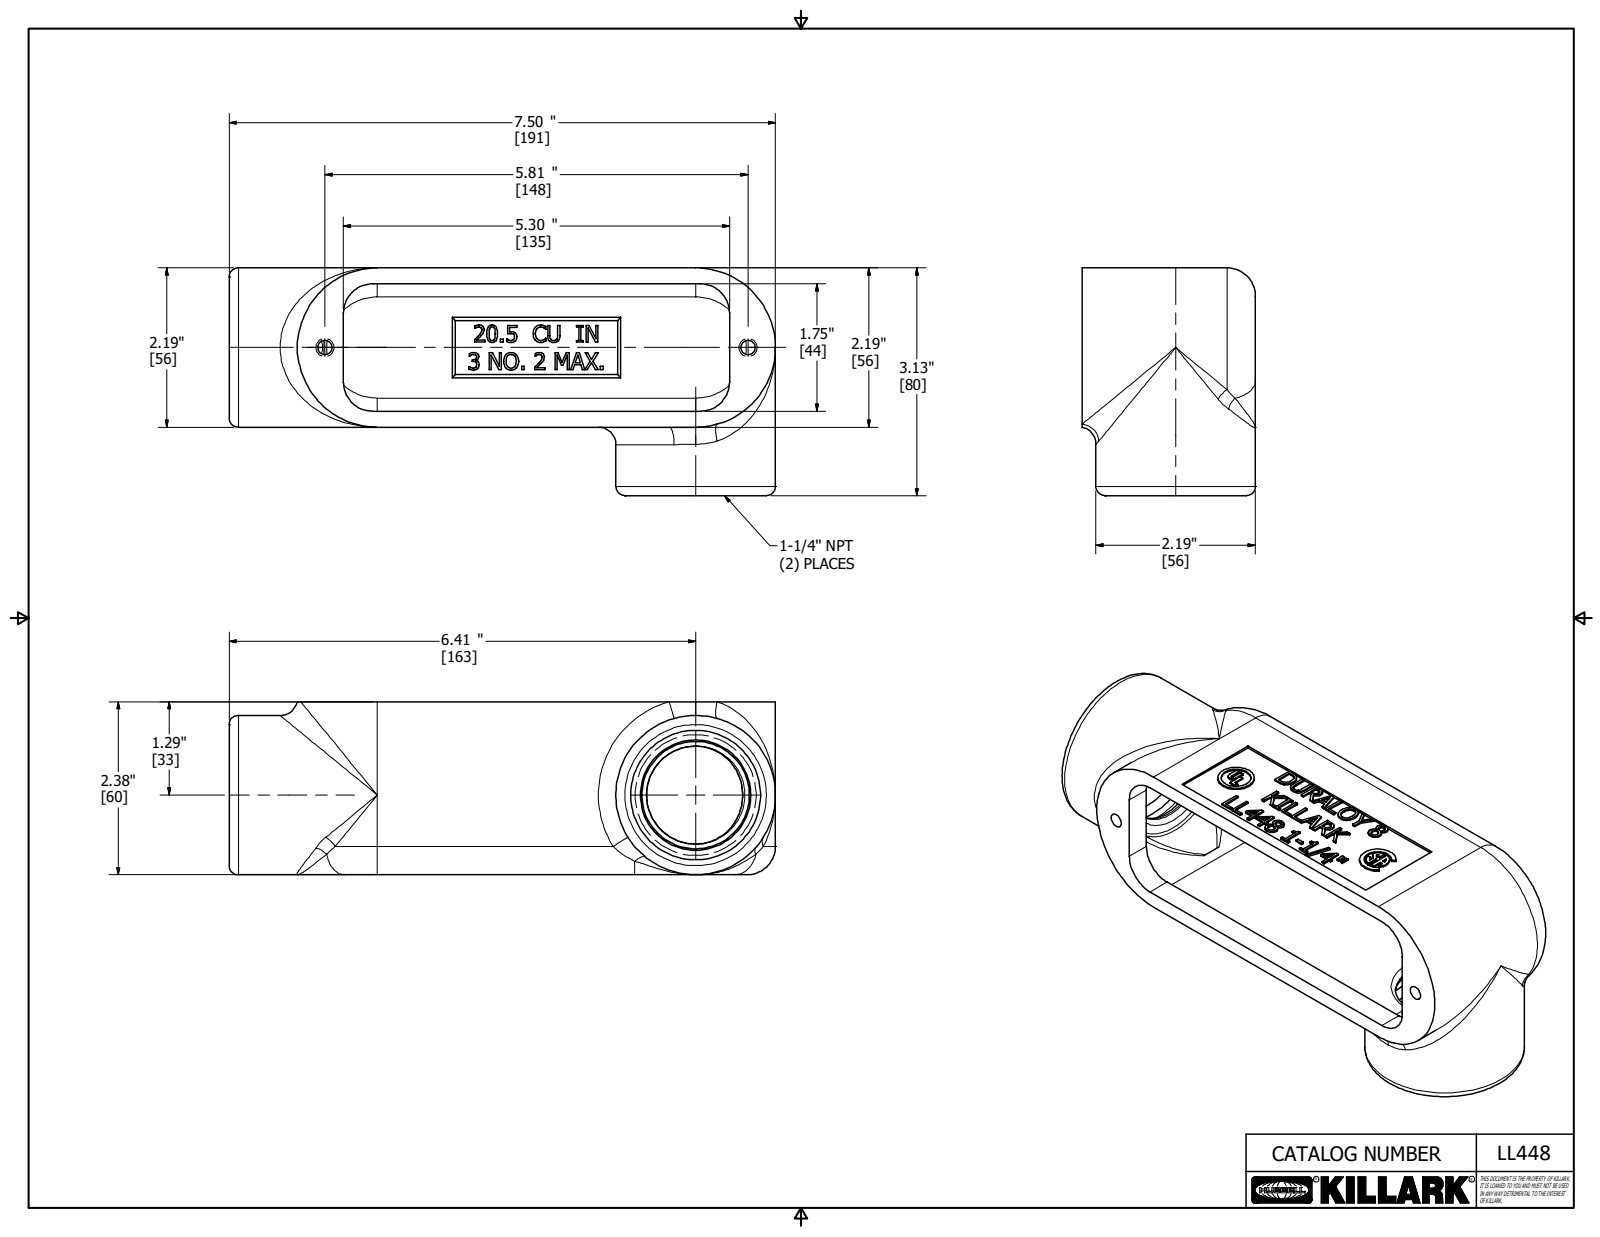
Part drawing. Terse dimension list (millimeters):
name: 21727-2
written by: Autodesk Inventor 2018 (AUTOMOTIVE_DESIGN)
unit: mm
bodies: 1 solid, 722 faces (447 planar, 36 cylindrical, 239 other)
size: 190.5 × 79.5 × 60.5
volume: 207 500 mm³; area: 74 710 mm²
holes: 2× ⌀5, 2× ⌀42.3, 1× ⌀10.3, 1× ⌀45.2
bosses: 2× ⌀55.6, 1× ⌀12.7
rounds: 4× R10.2, 2× R5.1, 2× R9.9, 2× R22.7, 2× R27.8, 1× R0.4, 1× R1.6, 1× R2.9
face distances: 5.1, 50.5, 45.5, 49.8, 60.5, 55.4, 55.6, 0.8, 54.9, 4.3
hole spacings: 91.3, 147.6
